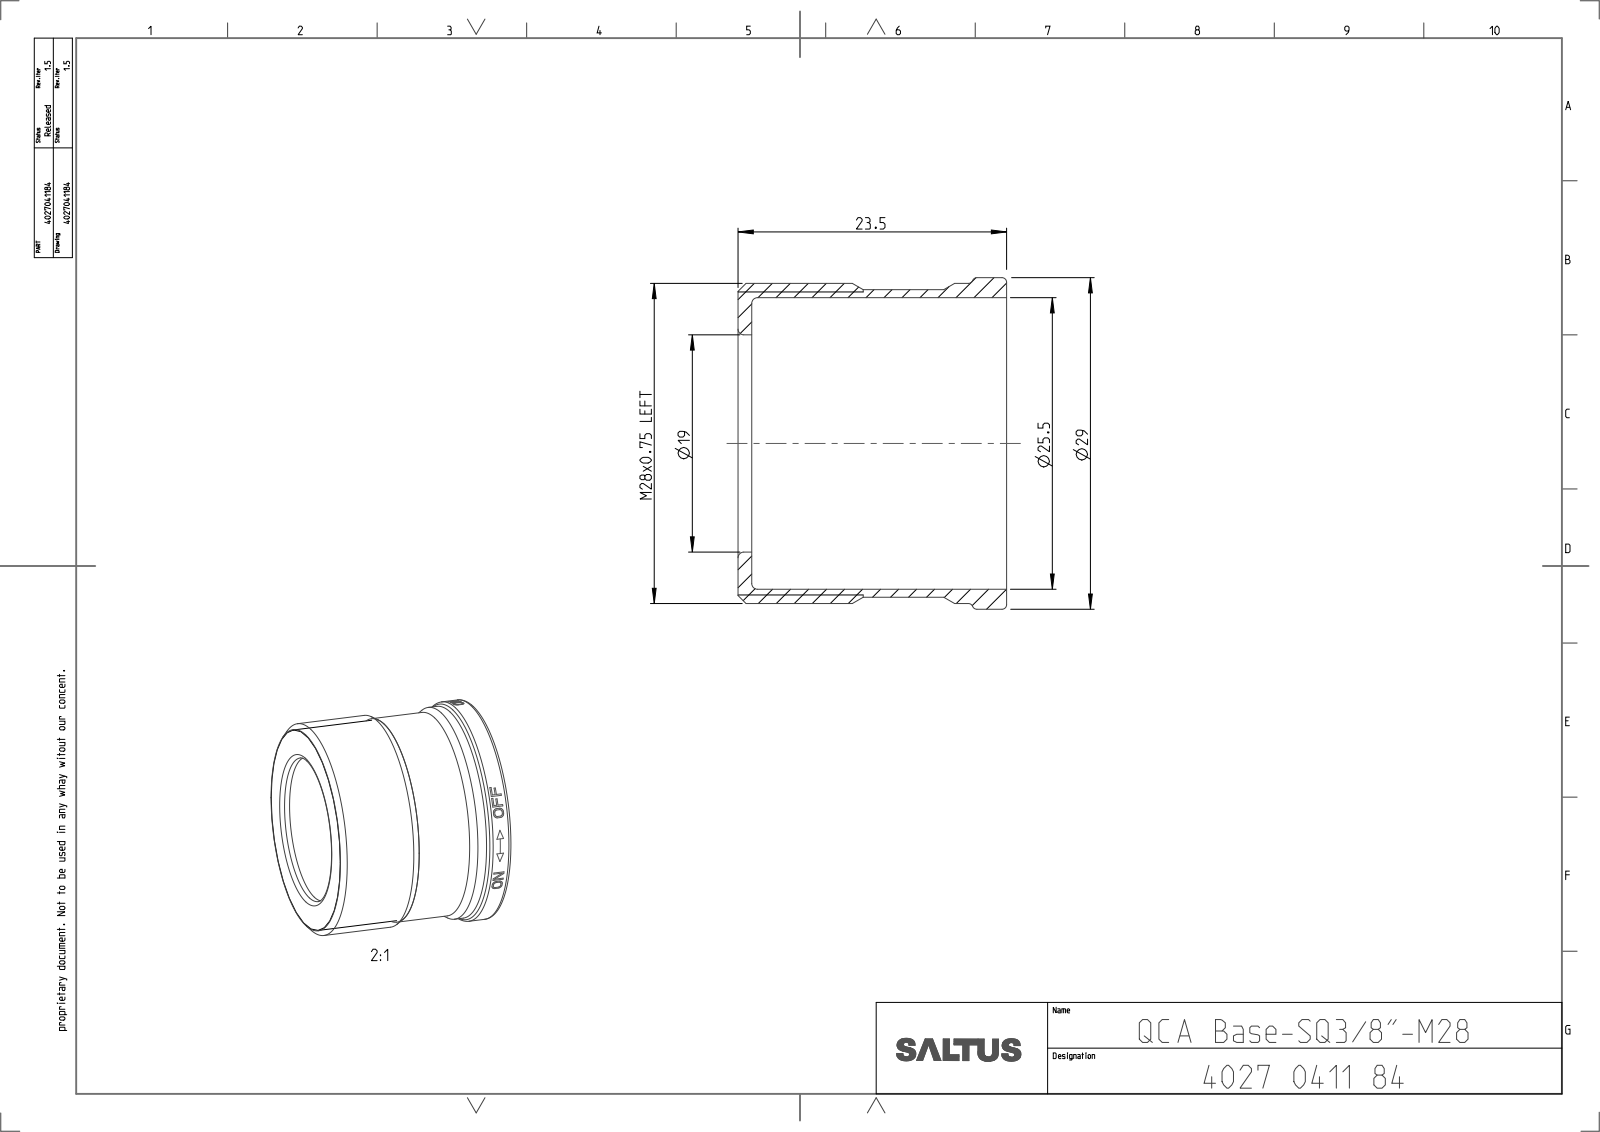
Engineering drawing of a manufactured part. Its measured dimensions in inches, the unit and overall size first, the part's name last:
Units: inches
Overall size (bounding box): 1.142 × 1.142 × 0.925
Round holes (diameter × count): ⌀0.748 ×1, ⌀1.004 ×1
Round bosses / shafts (diameter × count): ⌀1.142 ×1, ⌀1.102 ×1, ⌀1.059 ×1, ⌀1.043 ×1
Main face-to-face distances: 0.047, 0.878, 0.925, 0.494, 0.384, 0.431
Volume: 0.151 in³ · Surface area: 8.534 in²
Bodies: 1 solid, 34 faces (4 planar, 14 cylindrical, 16 other)
Part name (STEP PRODUCT): 4027041184
STEP written by: CREO PARAMETRIC BY PTC INC, 2022414 (CONFIG_CONTROL_DESIGN)
